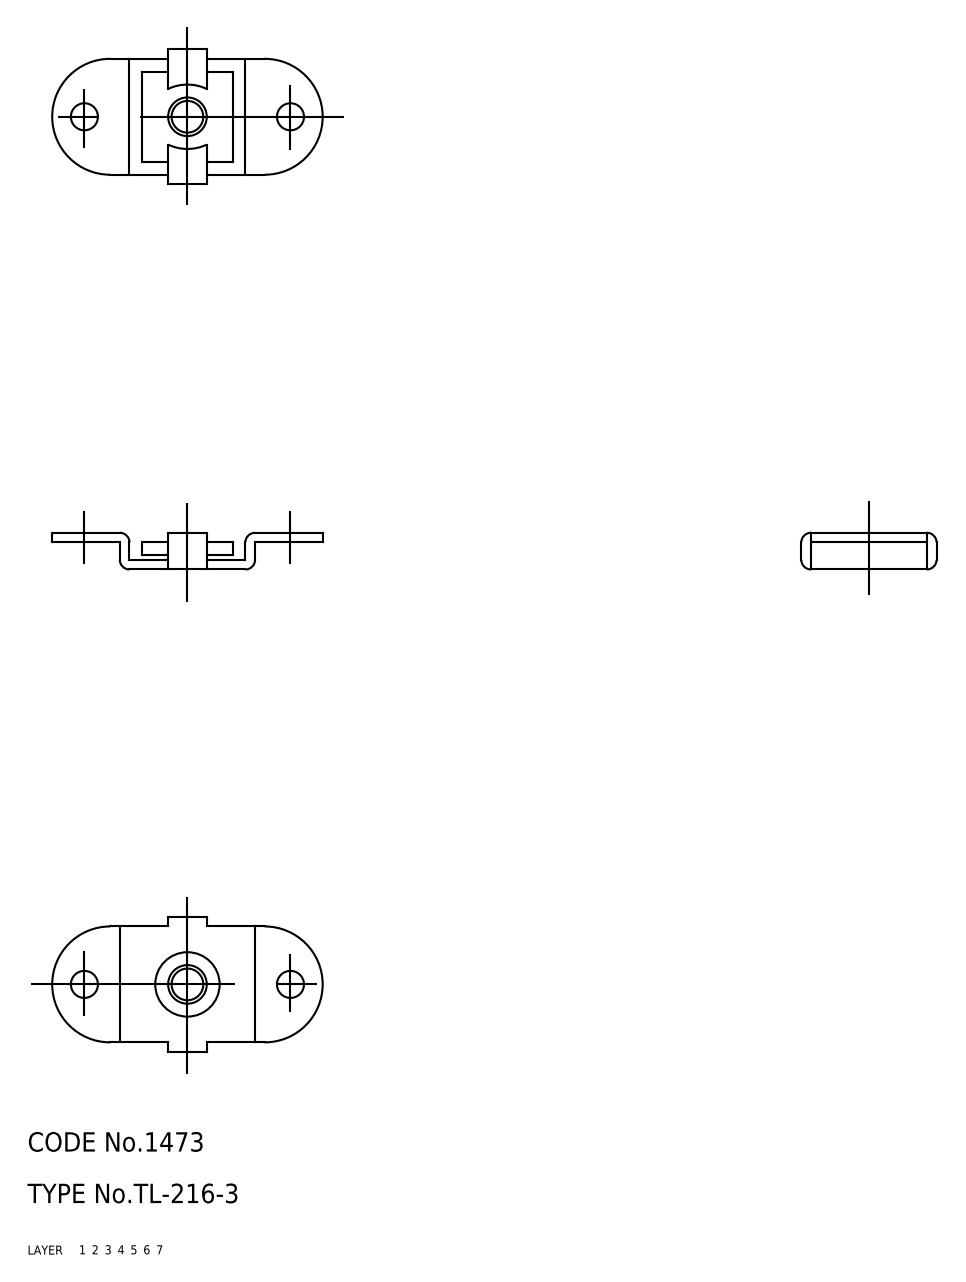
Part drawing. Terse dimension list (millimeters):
name: 67111387; 67111400
written by: CADfix (AUTOMOTIVE_DESIGN)
unit: mm
bodies: 2 solids, 52 faces (0 planar, 0 cylindrical, 52 other)
size: 42 × 21 × 5.7
volume: 1 564 mm³; area: 2 448 mm²
